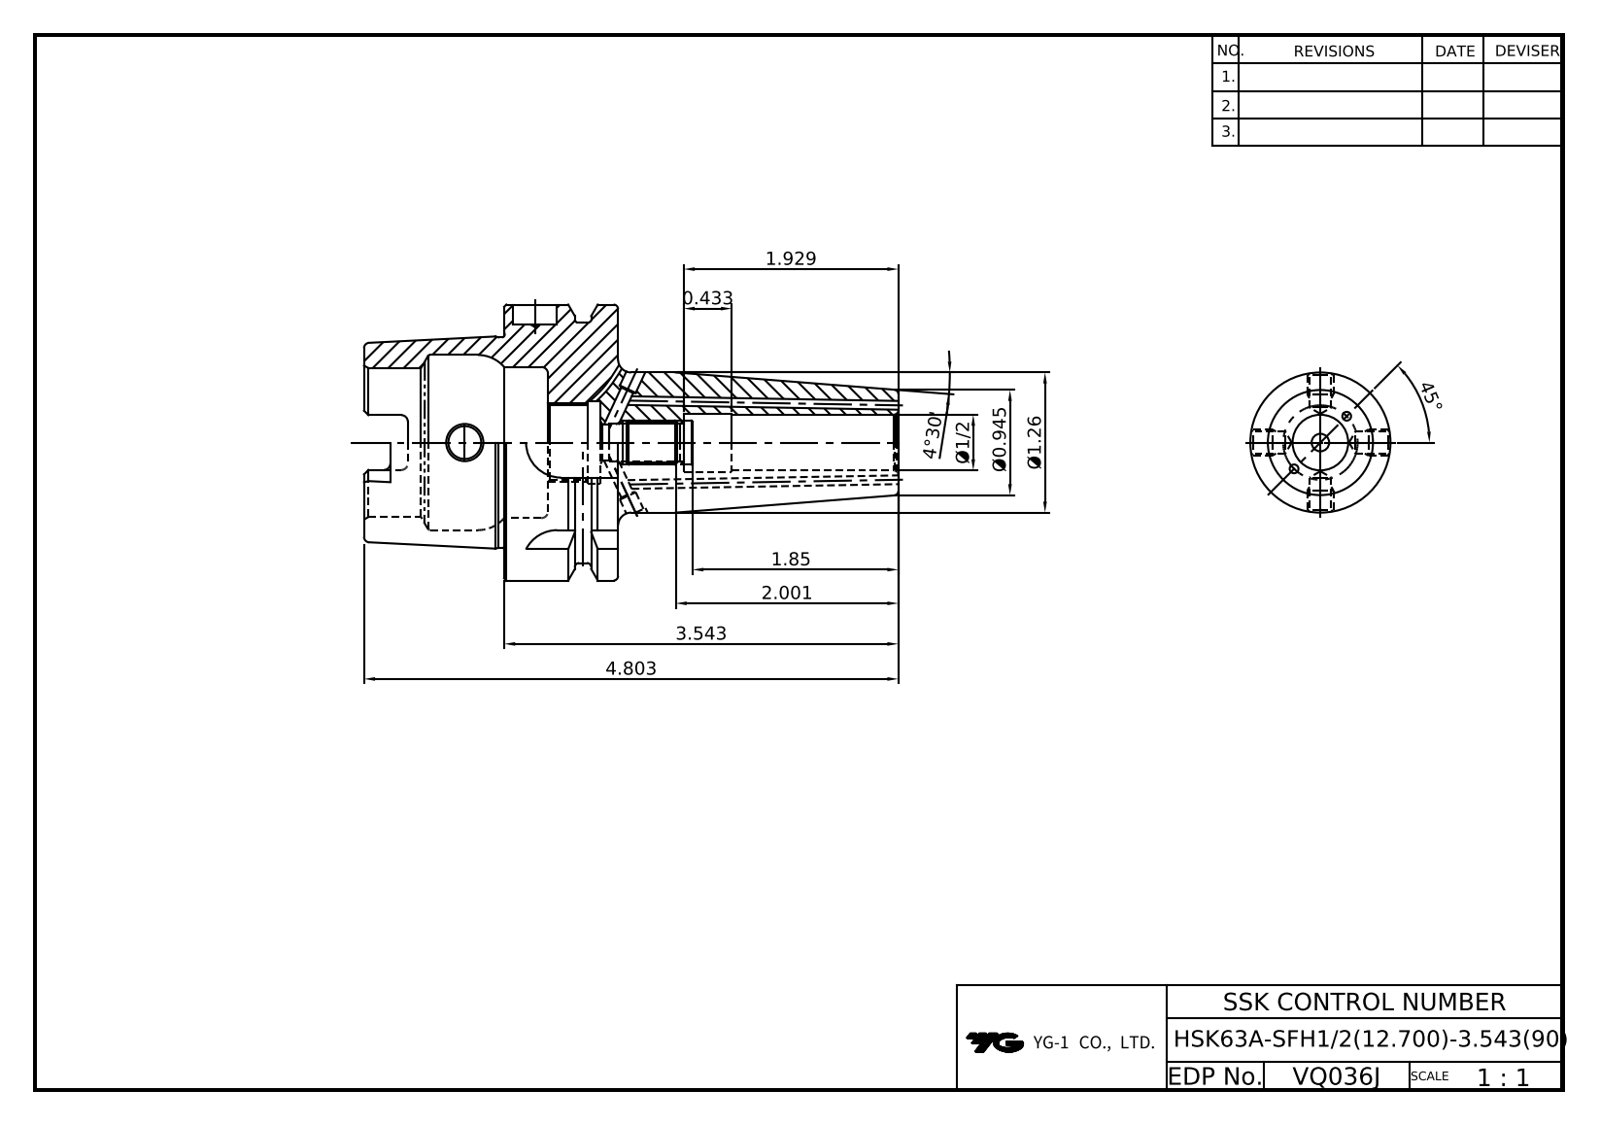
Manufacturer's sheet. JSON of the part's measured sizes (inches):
{"part_name": "VQ032J-HSK63A-SFH0_5C-3_543", "step_written_by": "PRO/ENGINEER BY PARAMETRIC TECHNOLOGY CORPORATION, 2012130 (CONFIG_CONTROL_DESIGN)", "units": "inches", "bodies": {"solids": 1, "faces": 202, "planar": 57, "cylindrical": 59, "other": 86}, "overall_size": [4.803, 2.48, 2.48], "volume_in3": 7.082, "surface_area_in2": 48.06, "round_holes": [[0.197, 2], [0.295, 1], [0.331, 1], [0.335, 1], [0.394, 1], [0.5, 1], [0.524, 1], [0.669, 1], [0.709, 1], [0.748, 1], [1.339, 1], [1.358, 1]], "round_bosses_or_shafts": [[2.48, 1], [2.165, 1], [1.891, 1], [1.26, 1]], "partial_cylinders_radius": [[0.059, 6], [0.113, 4], [0.315, 4]], "face_to_face_distances": [1.024, 0.394, 0.63, 1.26, 1.654, 2.283, 0.866, 2.087, 0.157, 0.472], "hole_center_spacings": [1.102, 1.732]}
